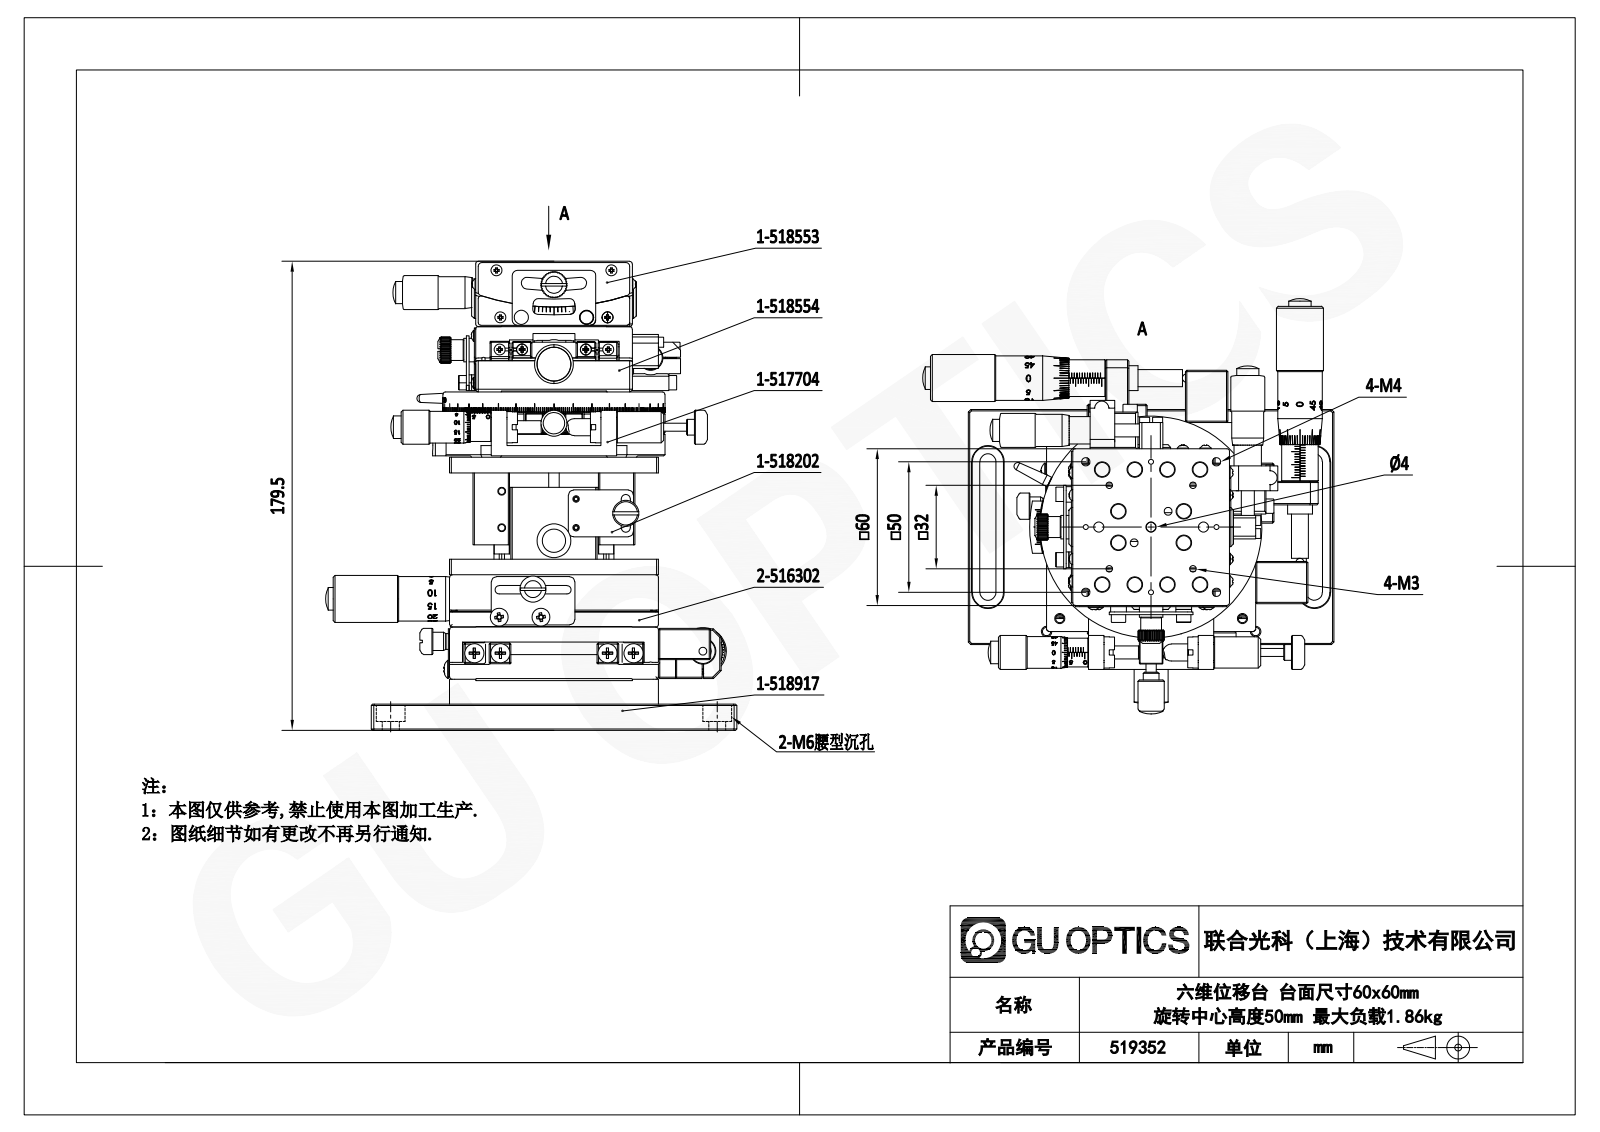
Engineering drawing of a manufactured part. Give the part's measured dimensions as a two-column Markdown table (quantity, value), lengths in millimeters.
| quantity | value |
| --- | --- |
| part name | 518202; 518553; 519352; 517704 (+4 more) |
| STEP written by | SolidWorks 2020 (CONFIG_CONTROL_DESIGN) |
| units | millimeters |
| bodies | 43 solids, 8904 faces (5797 planar, 1473 cylindrical, 1634 other) |
| overall size | 179.5 × 158.98 × 157.48 |
| volume | 723 269 mm³ |
| surface area | 333 799 mm² |
| round holes (diameter × count) | 6 × 60, 3.3 × 25, 2.5 × 23, 3.4 × 21, 3.5 × 20, 3.24 × 17, 3 × 14, 2.46 × 12, 5 × 12, 8 × 9, 4.4 × 8, 4.5 × 8 |
| round bosses / shafts (diameter × count) | 0.6 × 190, 5.5 × 40, 3 × 24, 6 × 10, 7.5 × 8, 4.35 × 8, 4.2 × 8, 4 × 6 |
| partial cylindrical surfaces (radius × count) | 1 × 65, 2 × 40, 1.5 × 8, 3.1 × 8, 1.65 × 4, 2.25 × 4, 3.5 × 4, 5.25 × 4 |
| main face-to-face distances | 10, 0.5, 49.5, 20, 25, 6, 9, 70, 14, 59.5 |
| hole center spacings | 25, 44.65, 16.49, 18.36, 24.38, 27.73, 28.18, 32.25 |
